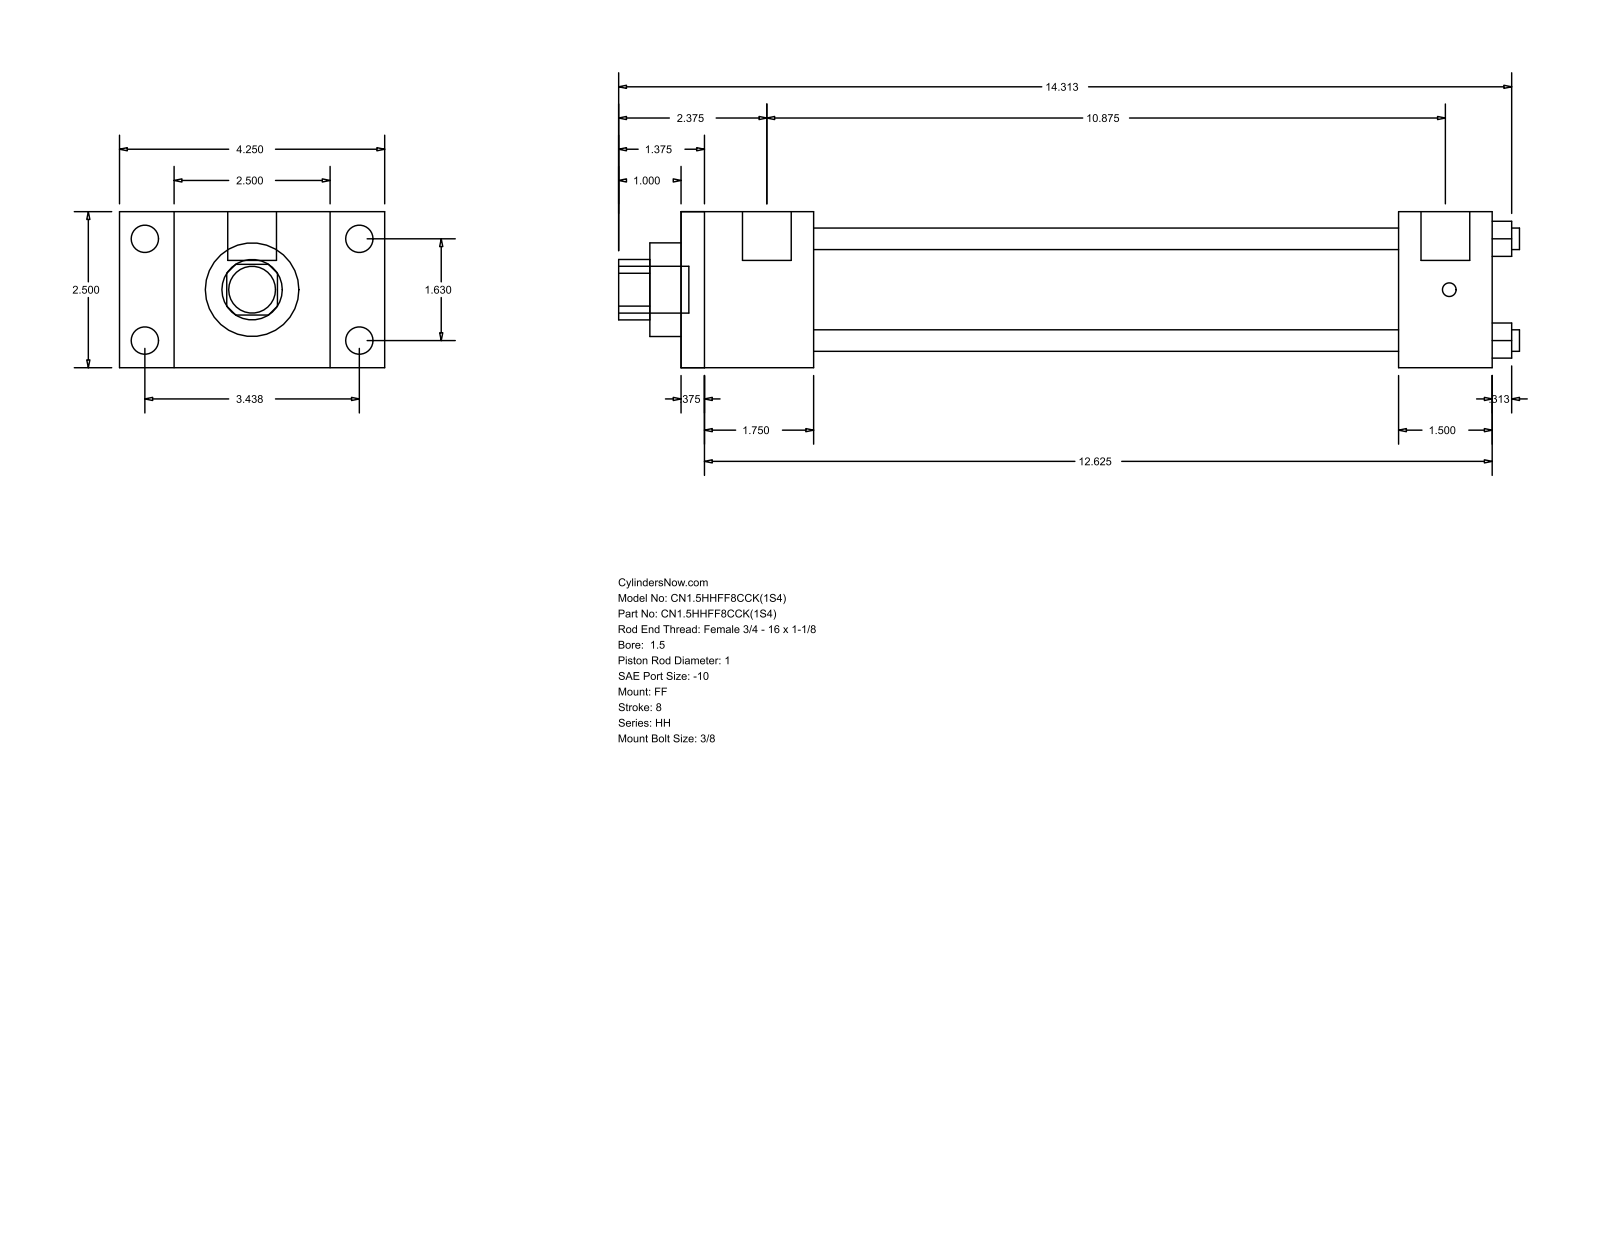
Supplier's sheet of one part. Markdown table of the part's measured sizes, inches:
| quantity | value |
| --- | --- |
| part name | HH_FF__0150_1 |
| STEP written by | GSSL Pune (CONFIG_CONTROL_DESIGN) |
| units | inches |
| bodies | 0 solids, 92 faces (64 planar, 28 cylindrical, 0 other) |
| overall size | 14.437 × 4.25 × 2.5 |
| round holes (diameter × count) | 0.345 × 4, 1 × 1, 1.5 × 1, 1.75 × 1 |
| round bosses / shafts (diameter × count) | 0.438 × 4, 0.219 × 4, 0.781 × 2, 0.75 × 1 |
| partial cylindrical surfaces (radius × count) | 0.484 × 1 |
| main face-to-face distances | 2.5, 13, 0.375, 12.625, 2.125, 1.75, 10.875, 11.5, 11.125, 9.375 |
| hole center spacings | 1.152, 1.63, 2.305 |
